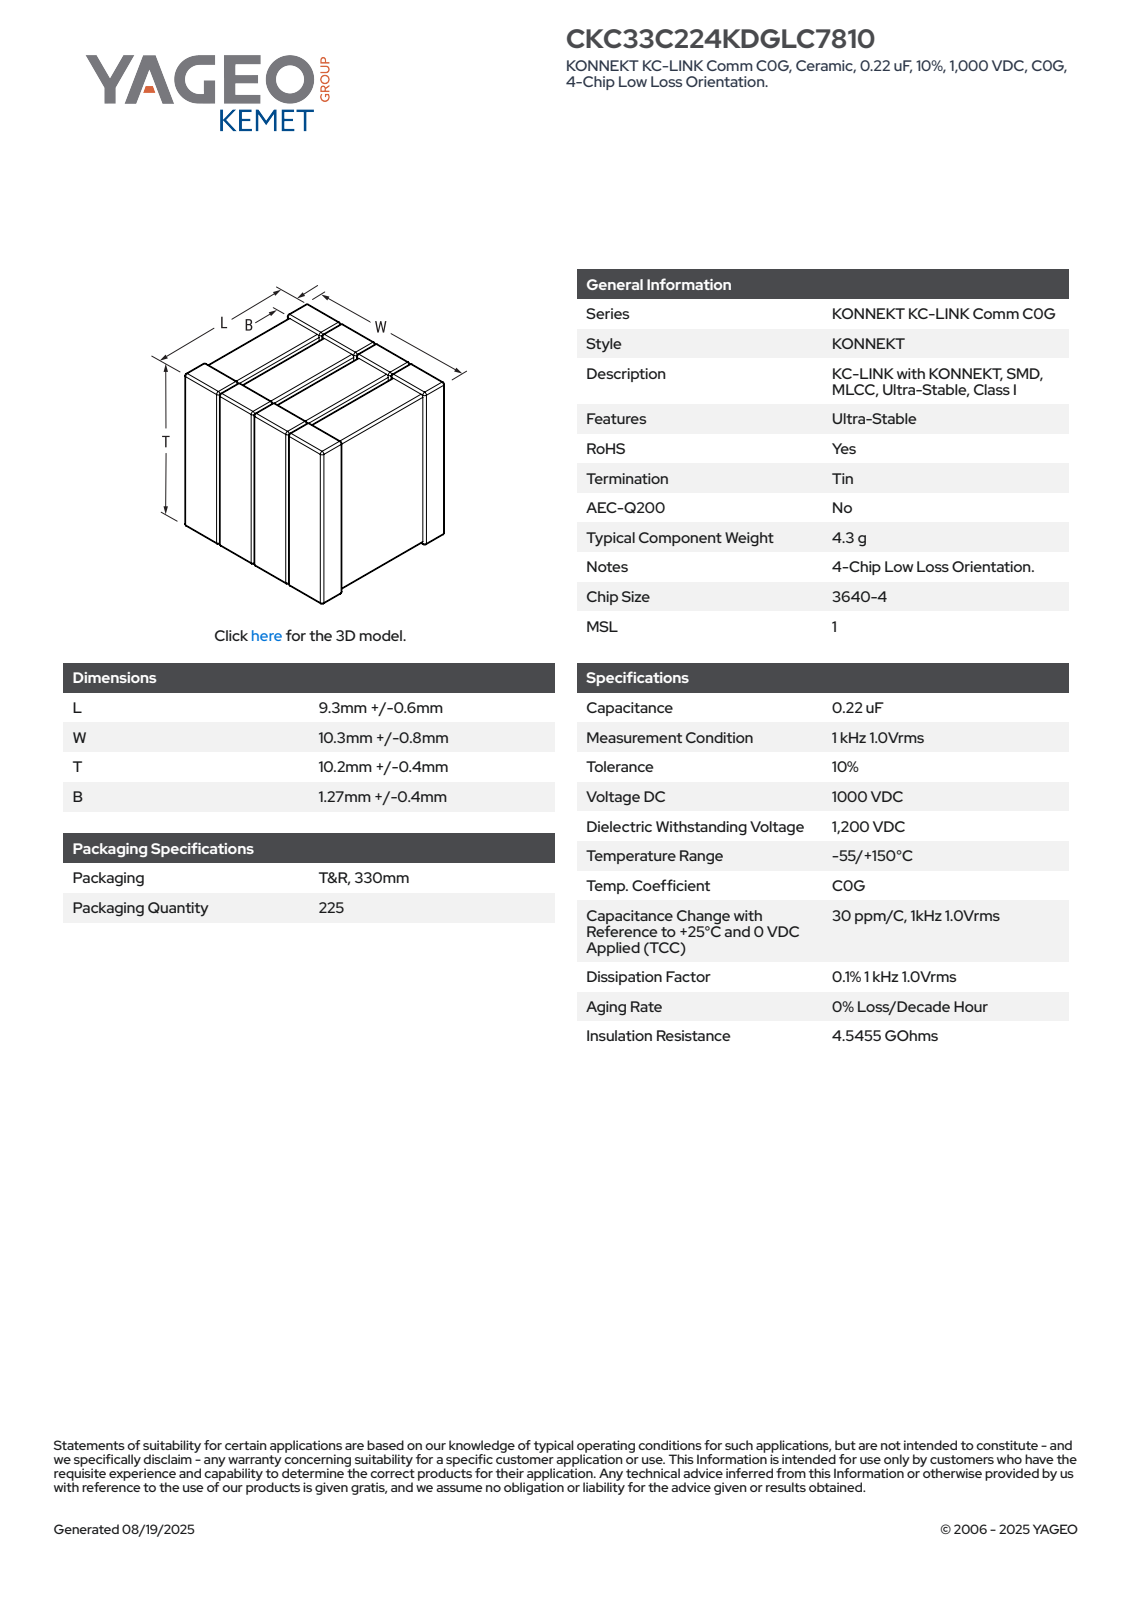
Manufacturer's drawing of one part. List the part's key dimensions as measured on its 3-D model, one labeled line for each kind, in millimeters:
Part name (STEP PRODUCT): CCSS_K4LL_3640_L9.9W11.1B1.67T10.6
STEP written by: SolidWorks 2021 (AUTOMOTIVE_DESIGN)
Units: millimetres
Bodies: 16 solids, 468 faces (284 planar, 120 cylindrical, 64 other)
Overall size (bounding box): 11.1 × 10.6 × 9.9
Volume: 1 063 mm³ · Surface area: 1 287 mm²
Partial cylindrical surfaces — rounded edges, fillets, slot ends (radius × count): R0.14 ×72
Main face-to-face distances: 2.78, 5.55, 2.63, 2.49, 2.92, 5.41, 2.77, 8.33, 8.04, 5.27
